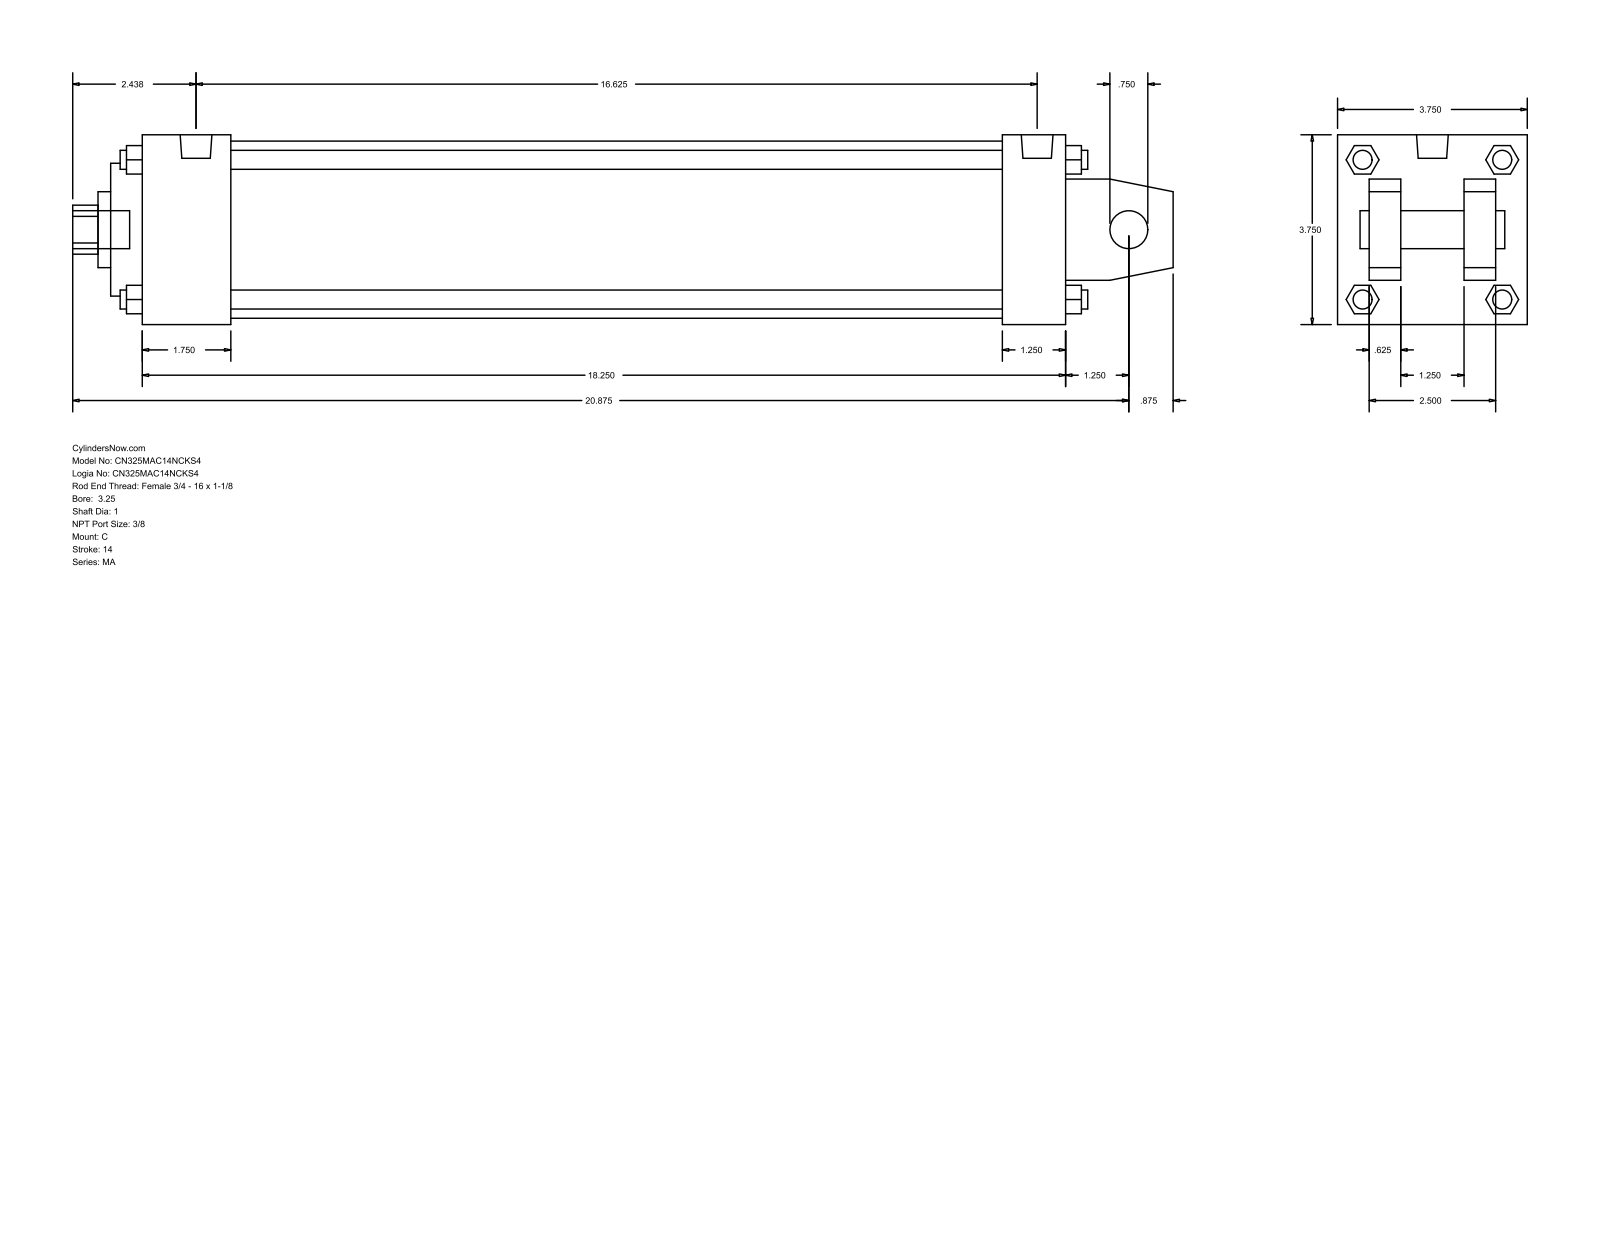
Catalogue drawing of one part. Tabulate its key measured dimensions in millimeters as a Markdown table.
| quantity | value |
| --- | --- |
| part name | MA_C__0325_1 |
| STEP written by | GSSL Pune (CONFIG_CONTROL_DESIGN) |
| units | millimeters |
| bodies | 0 solids, 141 faces (109 planar, 32 cylindrical, 0 other) |
| overall size | 552.45 × 95.25 × 95.25 |
| round holes (diameter × count) | 19.05 × 1, 25.4 × 1, 38.1 × 1, 66.67 × 1, 88.9 × 1 |
| round bosses / shafts (diameter × count) | 11.11 × 4, 9.53 × 4, 15.93 × 2, 19.05 × 1 |
| partial cylindrical surfaces (radius × count) | 12.29 × 1 |
| main face-to-face distances | 95.24, 15.87, 63.5, 463.56, 31.74, 79.37, 47.63, 431.81, 31.75, 44.46 |
